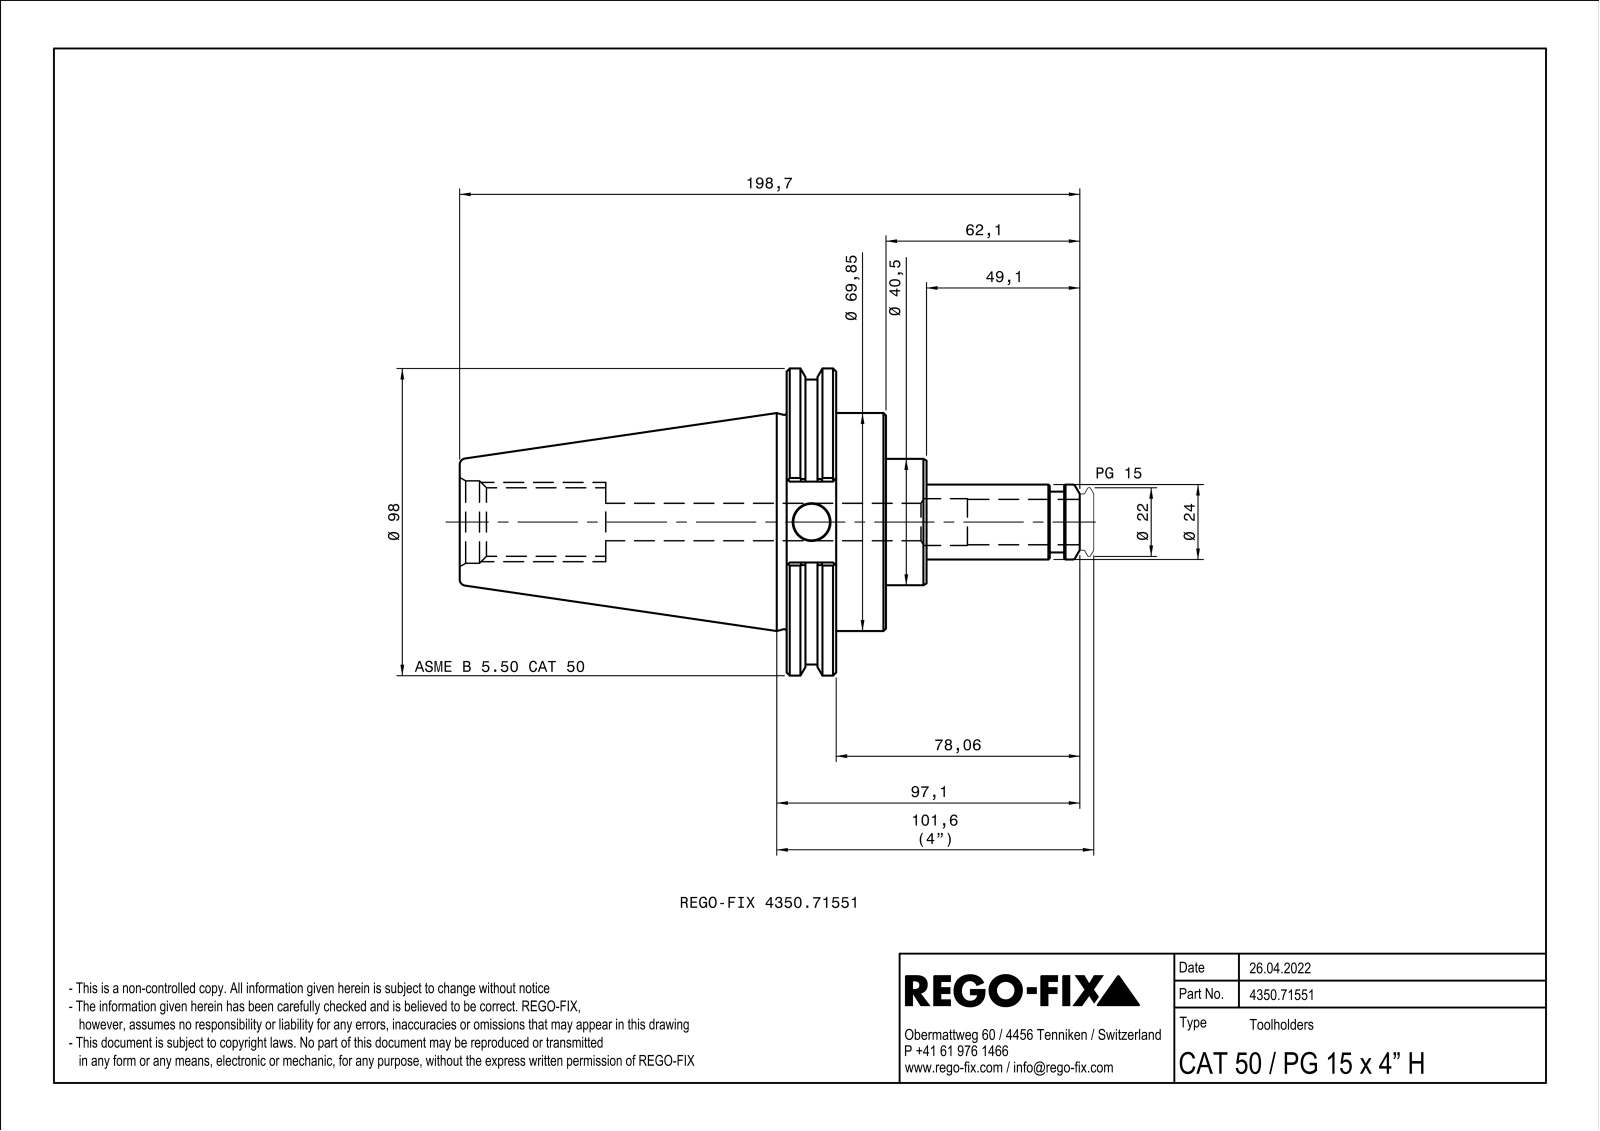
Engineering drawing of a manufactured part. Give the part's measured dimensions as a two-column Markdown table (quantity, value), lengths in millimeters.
| quantity | value |
| --- | --- |
| part name | NOCUT |
| STEP written by | SIEMENS PLM Software Solid Edge ST10 (AUTOMOTIVE_DESIGN) |
| units | millimeters |
| bodies | 1 solid, 119 faces (35 planar, 32 cylindrical, 52 other) |
| overall size | 198.7 × 98.42 × 94.39 |
| volume | 404 030 mm³ |
| surface area | 56 361 mm² |
| round holes (diameter × count) | 11.7 × 1, 12 × 1, 15 × 1, 21.96 × 1, 26.4 × 1 |
| round bosses / shafts (diameter × count) | 98.42 × 1, 91.3 × 1, 69.85 × 1, 40.5 × 1, 24 × 1, 19.5 × 1 |
| partial cylindrical surfaces (radius × count) | 0.5 × 12 |
| main face-to-face distances | 15.87, 15.96, 31.83, 13, 28.96, 44.83, 149.6, 136.6, 120.64, 104.77 |
